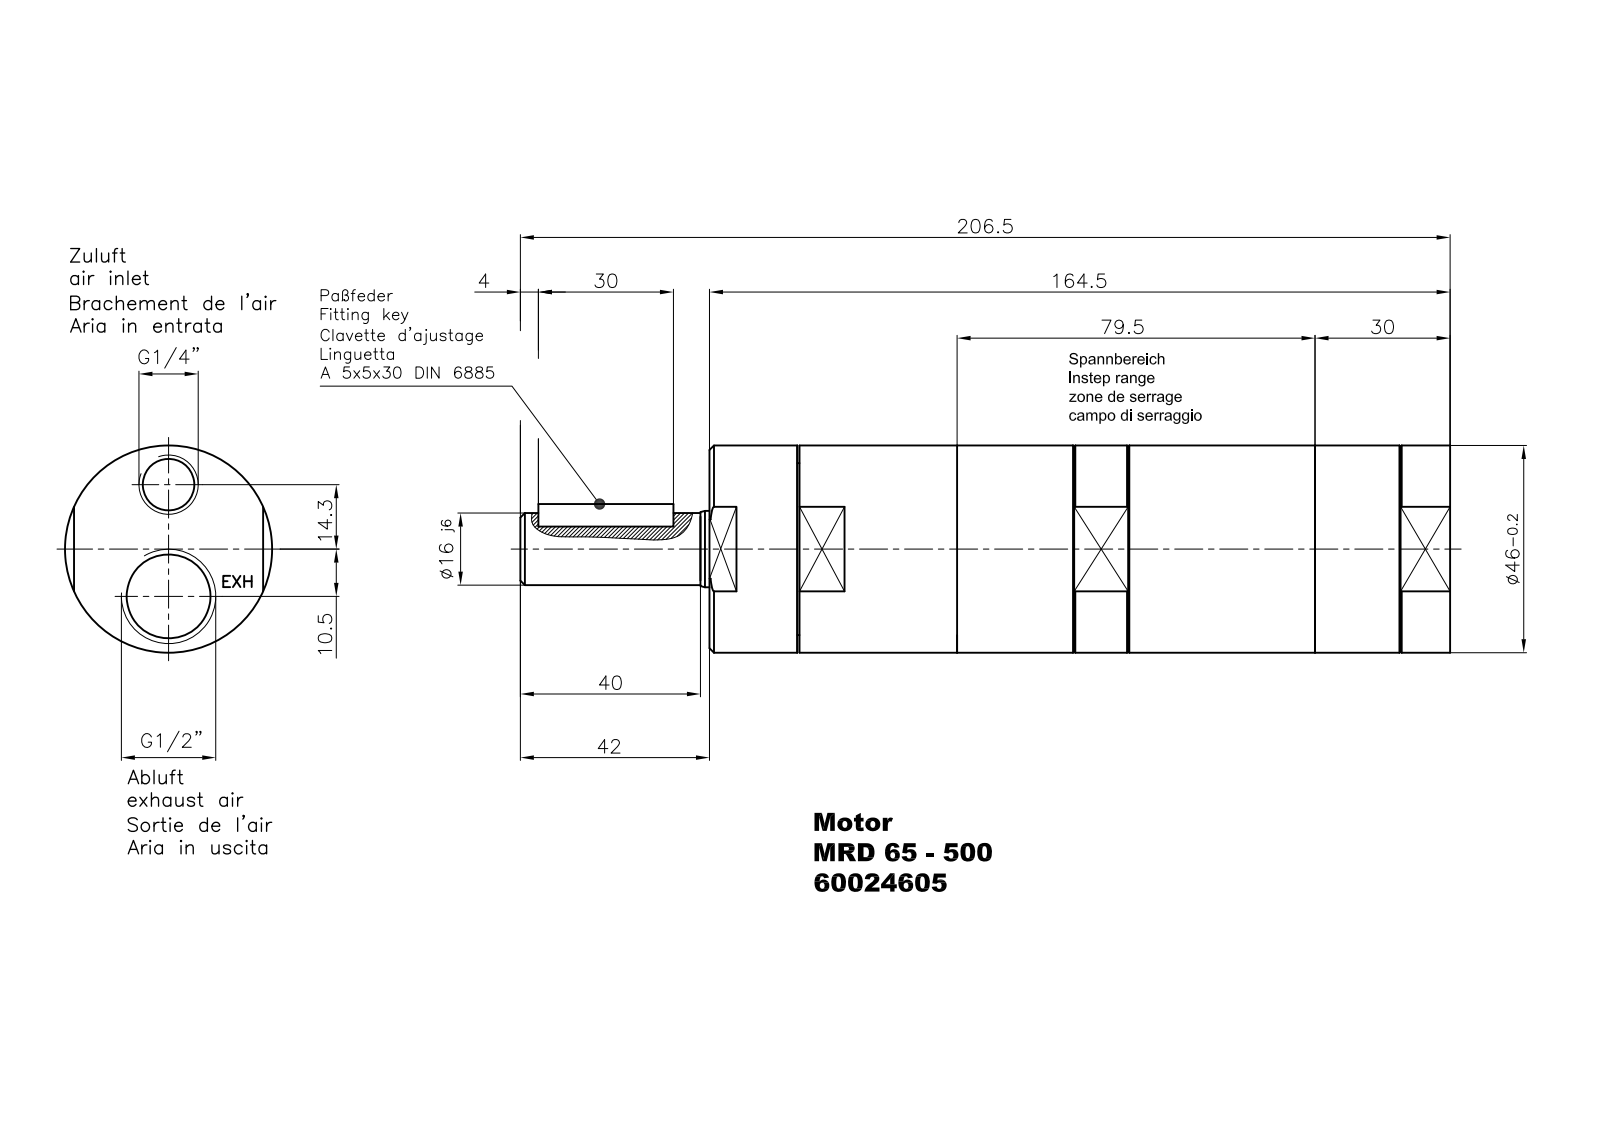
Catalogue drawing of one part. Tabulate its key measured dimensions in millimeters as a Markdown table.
| quantity | value |
| --- | --- |
| part name | MRD 65-206 |
| STEP written by | Autodesk Inventor 2012 (AUTOMOTIVE_DESIGN) |
| units | millimeters |
| bodies | 1 solid, 108 faces (73 planar, 18 cylindrical, 17 other) |
| overall size | 206.5 × 46 × 46 |
| volume | 274 649 mm³ |
| surface area | 32 940 mm² |
| round holes (diameter × count) | 1.6 × 1, 11.45 × 1, 17.5 × 1, 18.63 × 1 |
| round bosses / shafts (diameter × count) | 46 × 1, 38.16 × 1, 16.95 × 1, 16 × 1 |
| partial cylindrical surfaces (radius × count) | 2.5 × 2 |
| main face-to-face distances | 164.5, 42, 30, 134.5, 55, 109.5, 79.5, 19.5, 35.5, 115 |
| hole center spacings | 10.5, 14.3, 24.8 |
